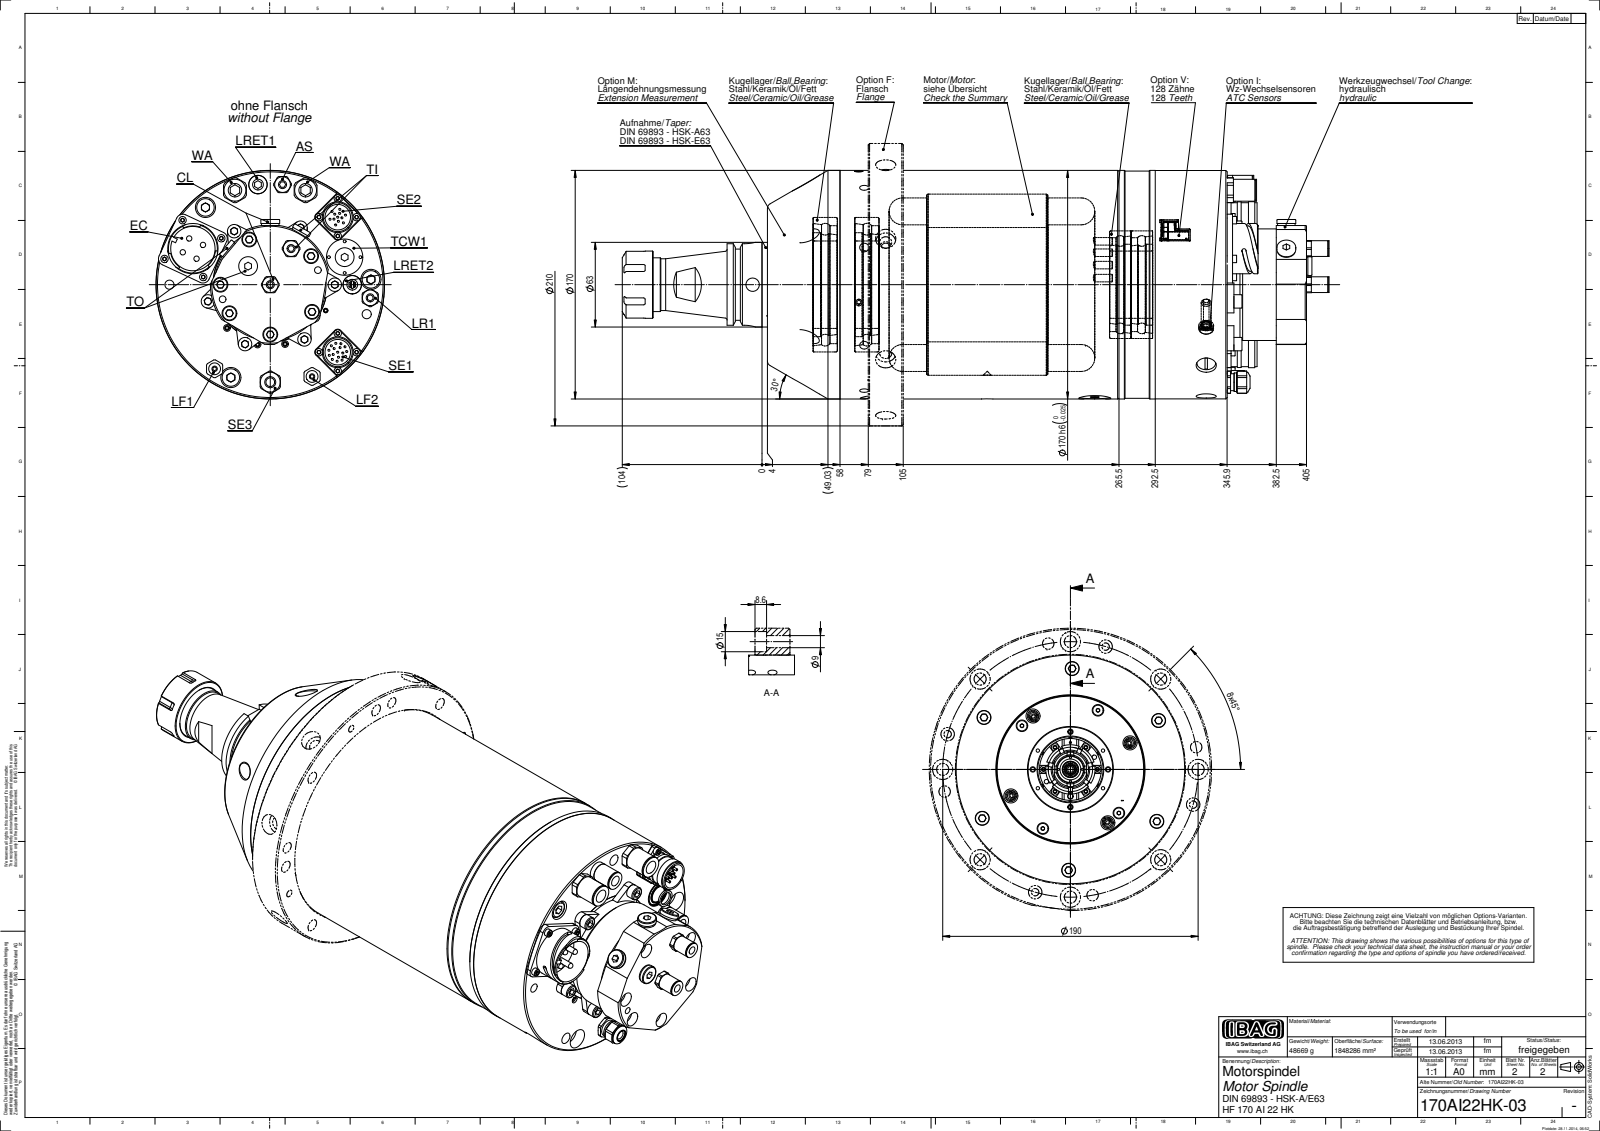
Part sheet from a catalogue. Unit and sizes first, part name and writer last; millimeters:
Units: millimetres
Overall size (bounding box): 526.13 × 170 × 170
Round holes (diameter × count): ⌀6.8 ×19, ⌀15 ×7, ⌀5 ×6, ⌀10.4 ×6, ⌀11 ×6, ⌀2.1 ×4, ⌀4.5 ×4, ⌀6 ×4, ⌀10 ×4, ⌀8.5 ×3, ⌀4 ×2, ⌀8 ×2
Round bosses / shafts (diameter × count): ⌀1.5 ×29, ⌀5.5 ×12, ⌀10 ×11, ⌀14 ×5, ⌀11.7 ×4, ⌀7.64 ×4, ⌀6 ×4, ⌀4 ×4
Partial cylindrical surfaces — rounded edges, fillets, slot ends (radius × count): R1 ×12, R6.6 ×6, R5 ×4, R8 ×4, R1.55 ×2, R9.25 ×2, R3 ×1, R8.25 ×1
Main face-to-face distances: 288, 234.5, 53.5, 54, 288.5, 342, 347, 401, 112.5, 59
Hole centre spacings: 75, 16, 129.91, 16.62, 45.5, 17.63, 23.5, 27.98
Bodies: 0 solids, 1420 faces (586 planar, 534 cylindrical, 300 other)
Part name (STEP PRODUCT): 170AI22HK-03
STEP written by: SolidWorks 2012 (CONFIG_CONTROL_DESIGN)
